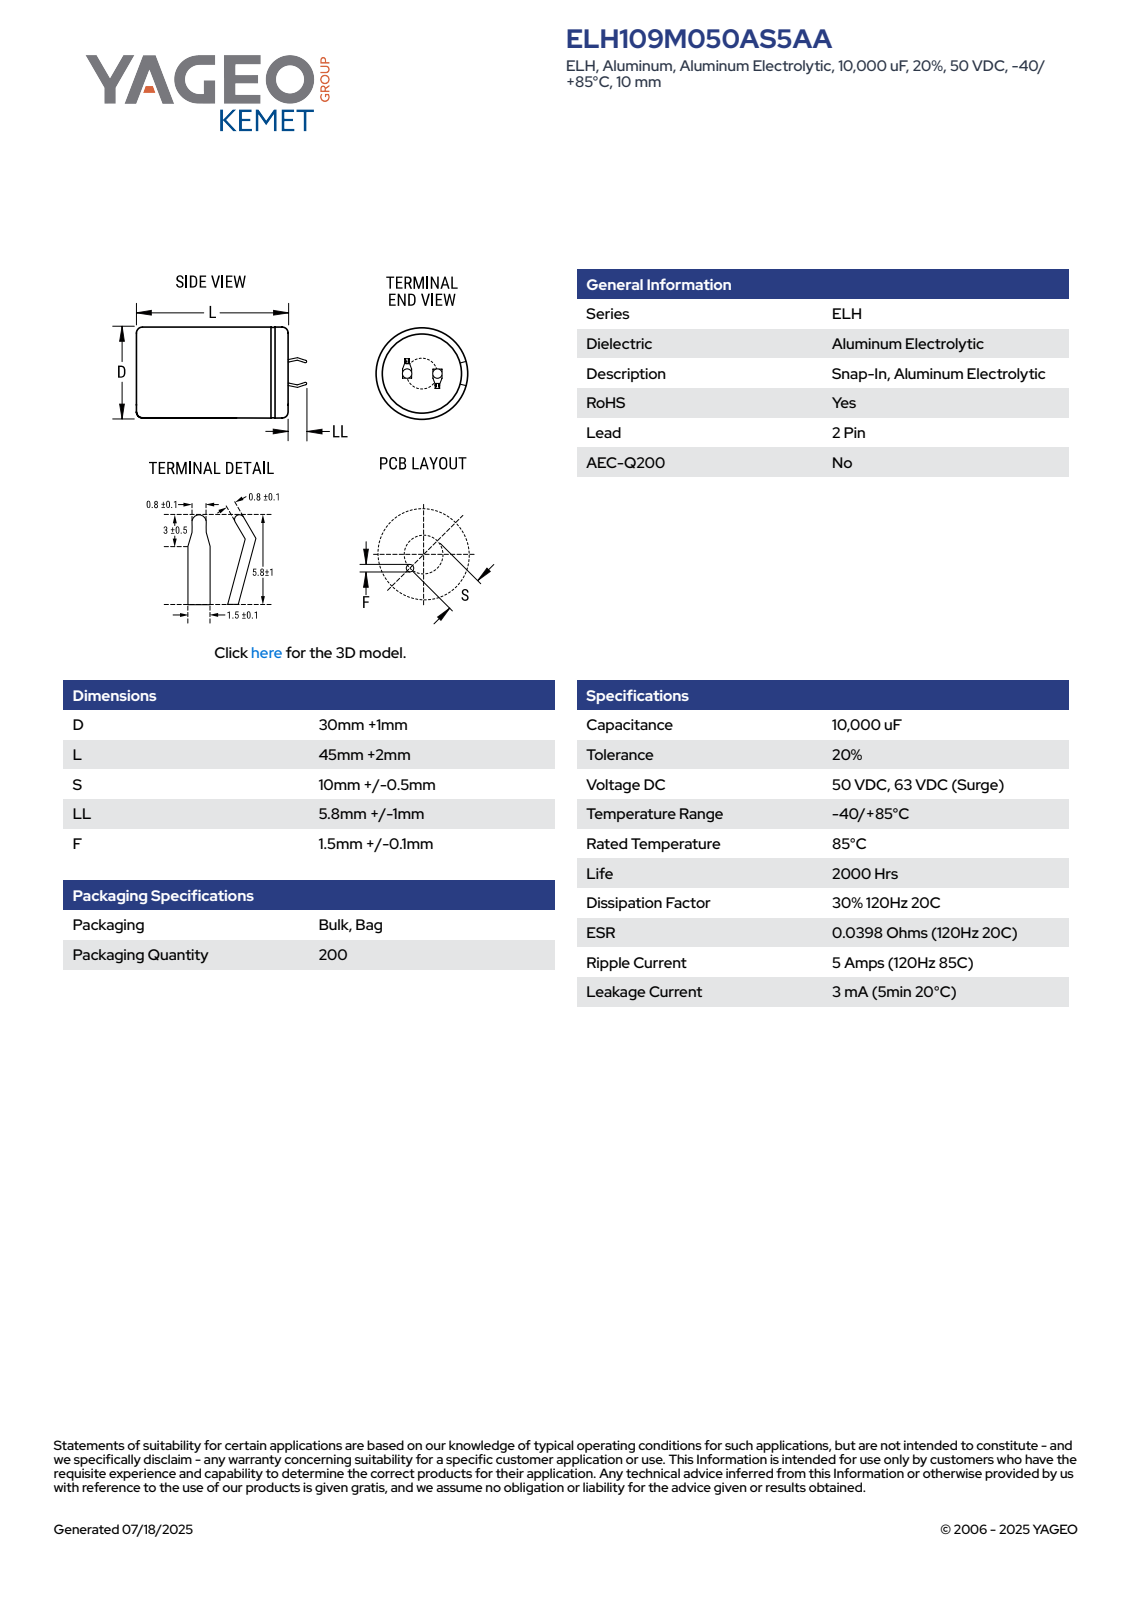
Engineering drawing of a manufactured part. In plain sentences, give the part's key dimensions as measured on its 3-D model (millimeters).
The part is named "CARS_K2P_30X45_D31L47S10LL6.8F1.6". Its 3-D file was written by "SolidWorks 2014 (AUTOMOTIVE_DESIGN)". It is 1 solid with 100 faces: 52 planar, 9 cylindrical and 39 other. Overall it measures 53.79 by 31 by 31 millimeters. Its volume is 35 140 cubic millimeters and its surface area 6 095 square millimeters. Round holes: 1 of diameter 27.43. Round bosses or shafts: 1 of diameter 31. Partial cylindrical surfaces (rounded edges, fillets, slot ends): 1 of radius 15.49. The main face-to-face distances are 46.99, 47.49, 0.5, 0.6, 7.08, 0.75, 1.35, 7.68, 6.48, 0.59.
